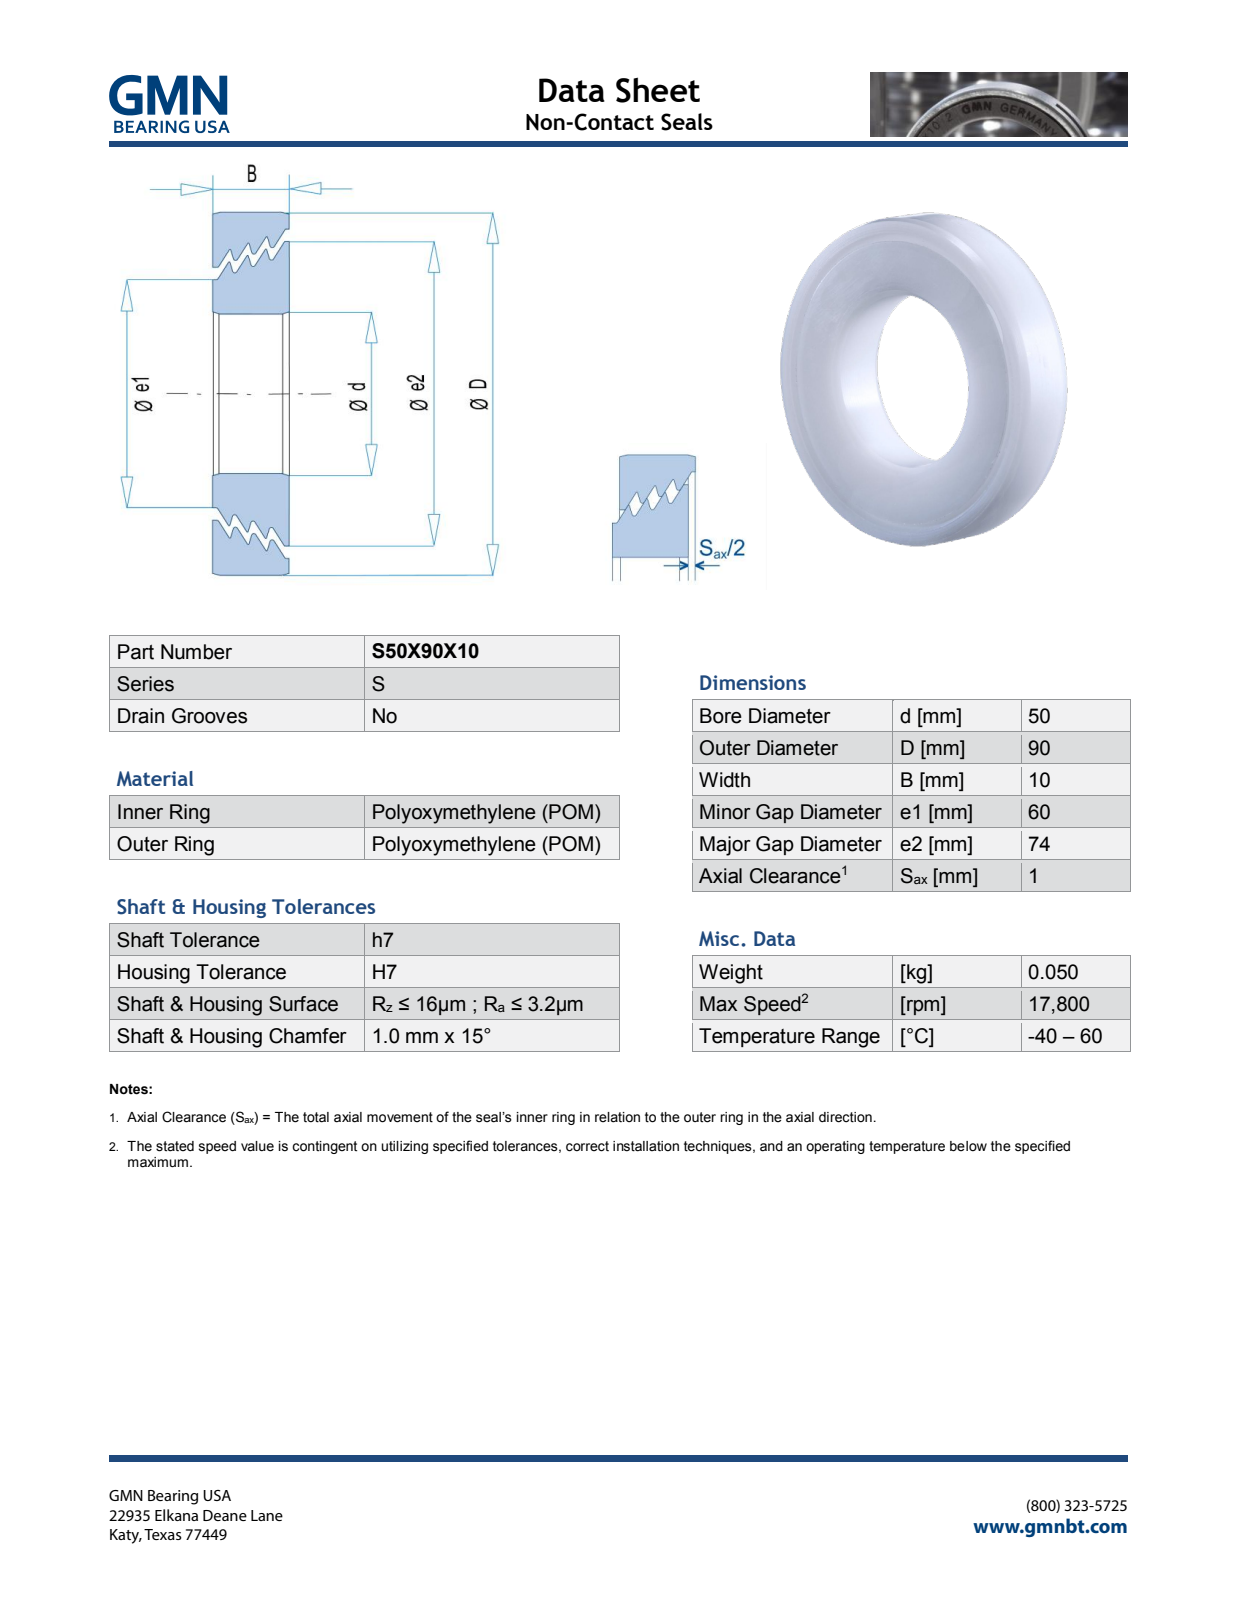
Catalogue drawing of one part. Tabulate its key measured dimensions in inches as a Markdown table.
| quantity | value |
| --- | --- |
| part name | S50X90X10_PRT |
| STEP written by | PRO/ENGINEER BY PARAMETRIC TECHNOLOGY CORPORATION, 2013150 (AUTOMOTIVE_DESIGN) |
| units | inches |
| bodies | 2 solids, 688 faces (608 planar, 12 cylindrical, 68 other) |
| overall size | 3.543 × 3.543 × 0.396 |
| volume | 2.571 in³ |
| surface area | 32.82 in² |
| round holes (diameter × count) | 1.969 × 1, 2.426 × 1, 2.978 × 1 |
| round bosses / shafts (diameter × count) | 3.543 × 1, 2.913 × 1, 2.362 × 1 |
| main face-to-face distances | 0.394, 0.396, 0.017, 0.131, 0.016, 0.115, 0.093, 0.014, 0.098, 0.017 |
